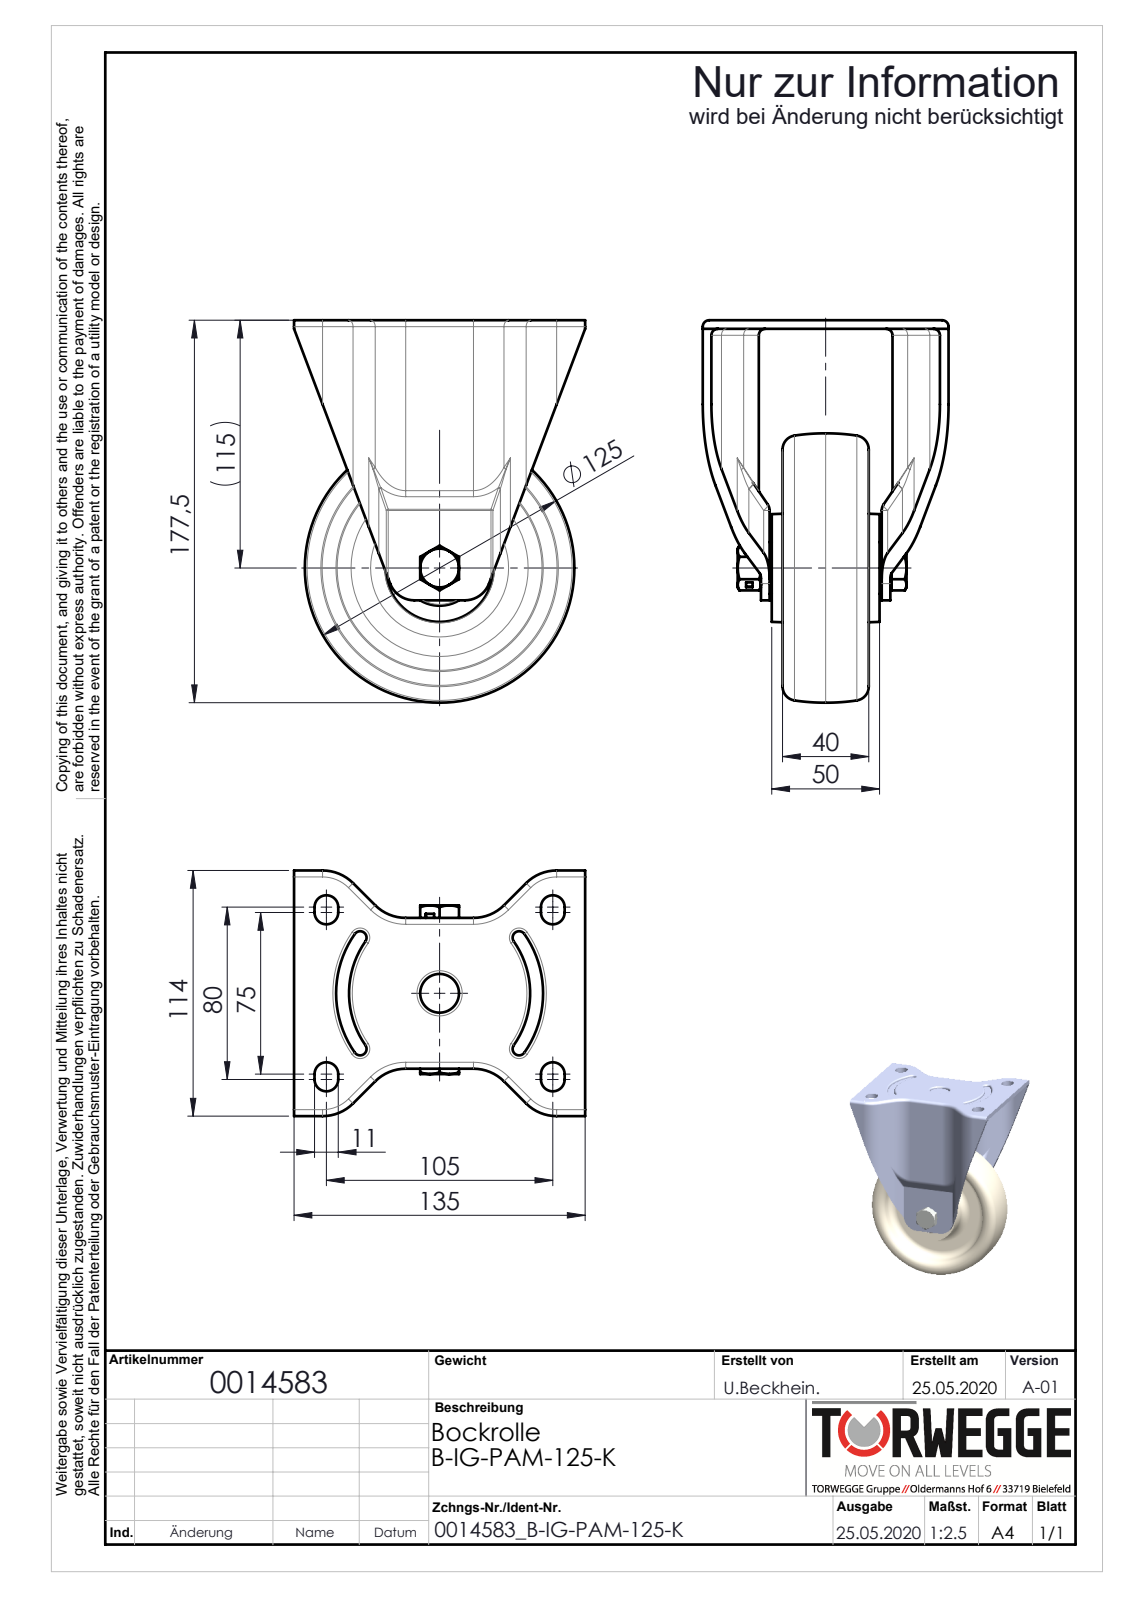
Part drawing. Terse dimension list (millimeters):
name: 0014583
written by: SolidWorks 2018 (AUTOMOTIVE_DESIGN)
unit: mm
bodies: 16 solids, 483 faces (131 planar, 184 cylindrical, 168 other)
size: 177.5 × 135 × 114
volume: 477 350 mm³; area: 153 782 mm²
holes: 1× ⌀10.2, 1× ⌀12, 1× ⌀12.1, 1× ⌀12.2, 1× ⌀15, 1× ⌀18, 1× ⌀20.3, 1× ⌀28.48, 1× ⌀29.7, 1× ⌀30
bosses: 1× ⌀35, 1× ⌀24, 1× ⌀21.52, 1× ⌀18, 1× ⌀14.95
rounds: 20× R3, 16× R1, 16× R5, 8× R5.5, 8× R20, 4× R16, 4× R21, 4× R24
face distances: 4, 5, 61, 30, 56, 1, 9, 10, 21, 40
